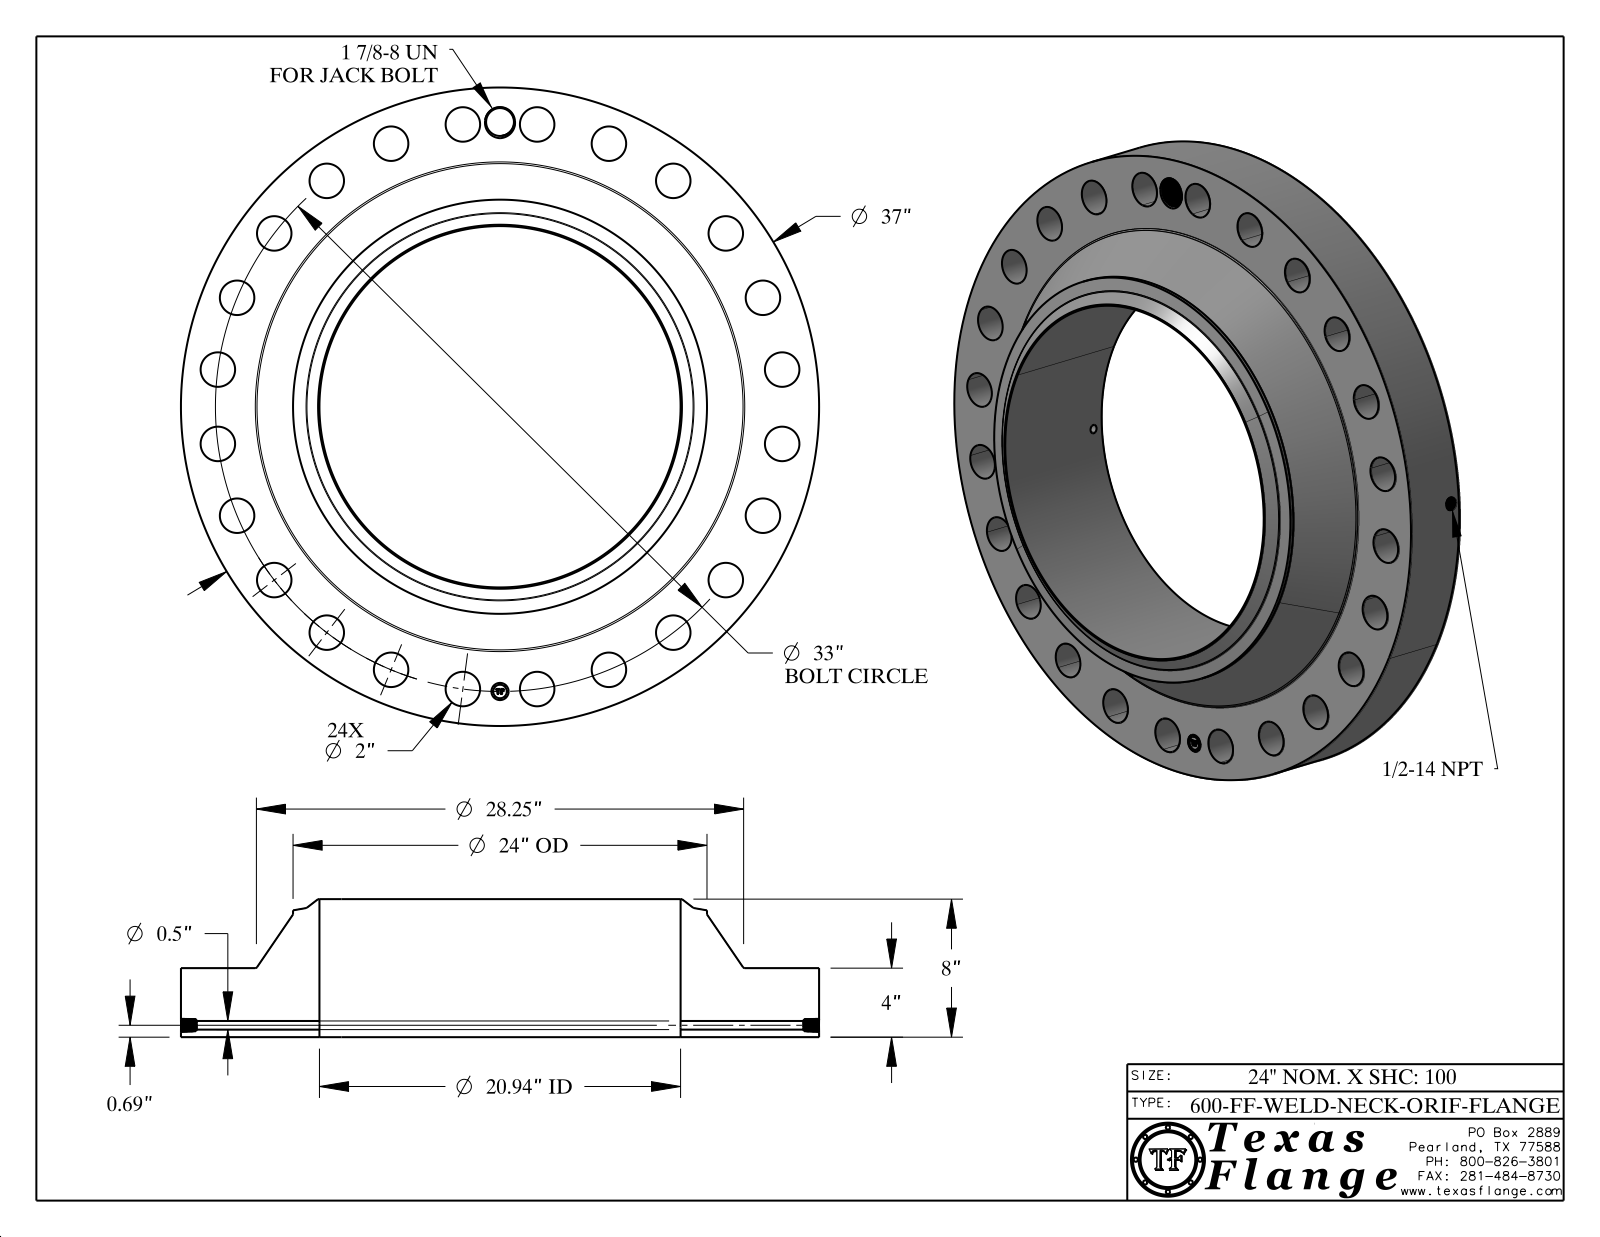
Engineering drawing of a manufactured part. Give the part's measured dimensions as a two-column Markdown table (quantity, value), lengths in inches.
| quantity | value |
| --- | --- |
| part name | 600-FF-WELD-NECK |
| STEP written by | CATIA V5 STEP AP214 (AUTOMOTIVE_DESIGN) |
| units | inches |
| bodies | 1 solid, 904 faces (368 planar, 157 cylindrical, 379 other) |
| overall size | 37 × 37 × 8 |
| volume | 3 260 in³ |
| surface area | 3 144 in² |
| round holes (diameter × count) | 2 × 24, 0.5 × 1, 0.672 × 1, 1 × 1, 1.615 × 1, 20.938 × 1 |
| round bosses / shafts (diameter × count) | 0.061 × 8, 37 × 1, 24 × 1, 0.788 × 1 |
| main face-to-face distances | 4, 8, 3.985, 0.015, 4.015, 0.298, 0.293, 0.054, 0.248, 0.193 |
| hole center spacings | 16.5, 8.541, 20.089, 28.579, 12.628, 4.307, 23.334, 26.181 |
